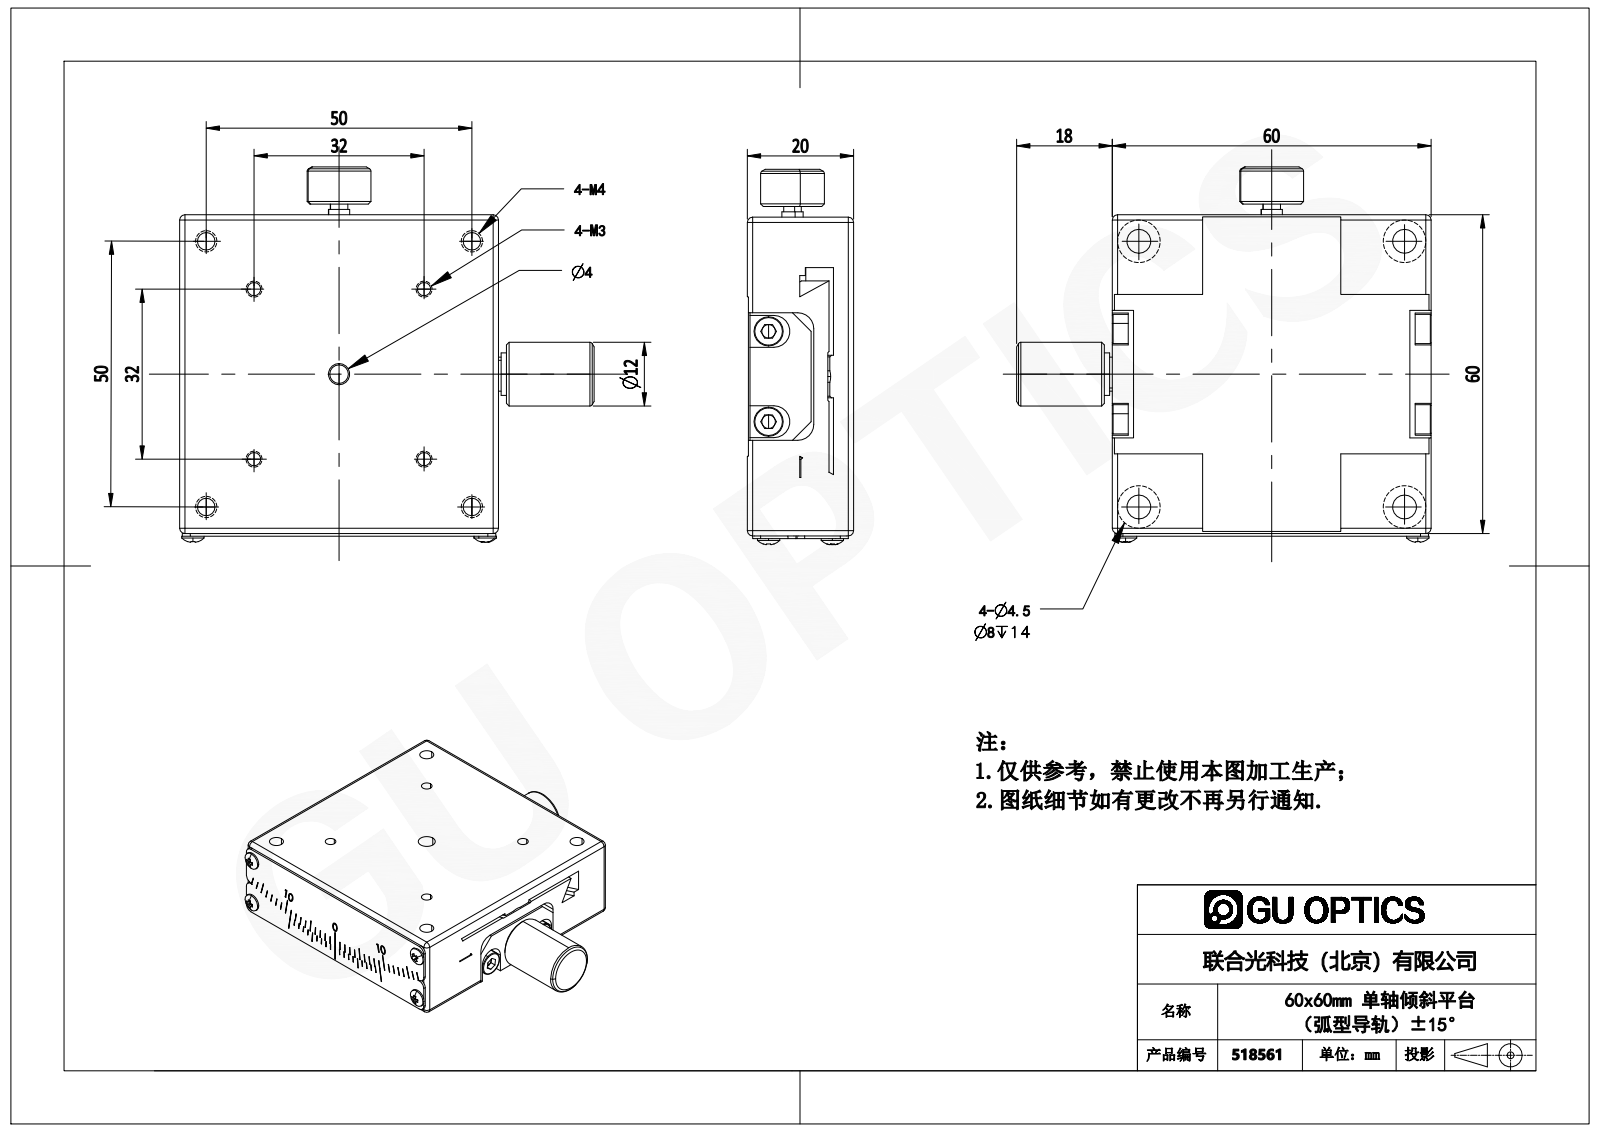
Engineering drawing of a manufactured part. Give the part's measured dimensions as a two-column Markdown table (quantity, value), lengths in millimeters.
| quantity | value |
| --- | --- |
| part name | MXG6-80CS |
| STEP written by | SolidWorks 2020 (CONFIG_CONTROL_DESIGN) |
| units | millimeters |
| bodies | 1 solid, 830 faces (485 planar, 173 cylindrical, 172 other) |
| overall size | 78 × 70.64 × 20 |
| volume | 70 286 mm³ |
| surface area | 21 799 mm² |
| round holes (diameter × count) | 2.5 × 4, 3.3 × 4, 4.5 × 4, 8 × 4, 1.6 × 1, 3.5 × 1, 4 × 1 |
| round bosses / shafts (diameter × count) | 4.2 × 4, 12 × 2, 5.5 × 2, 8 × 1, 6.4 × 1, 4 × 1, 3.3 × 1 |
| partial cylindrical surfaces (radius × count) | 1 × 12, 1.5 × 8, 3 × 4, 3.38 × 1, 4.5 × 1, 89 × 1, 89.5 × 1, 89.65 × 1 |
| main face-to-face distances | 19.8, 60.5, 60, 20, 7.5, 0.5, 9.5, 51, 12, 7 |
| hole center spacings | 41.98, 12.73, 22.63, 32, 35.36, 50, 57.98, 45.25 |
